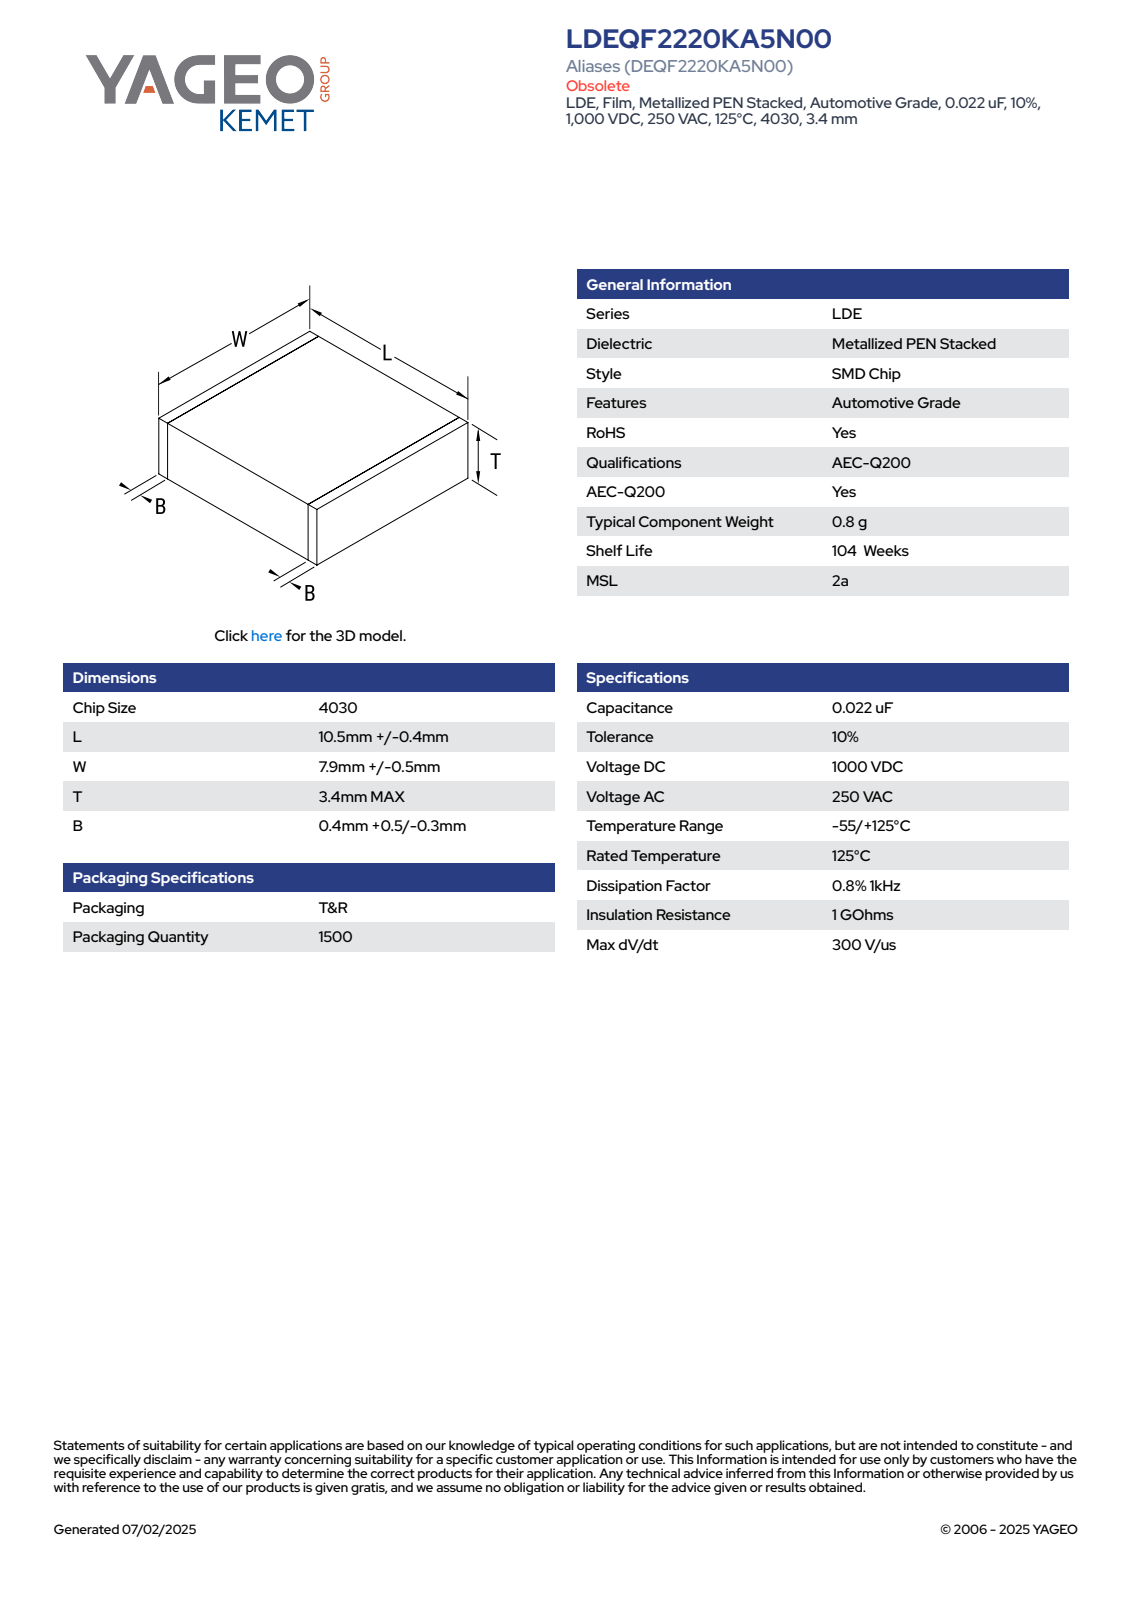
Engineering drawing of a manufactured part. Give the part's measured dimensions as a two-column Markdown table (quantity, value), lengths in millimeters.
| quantity | value |
| --- | --- |
| part name | CFS_LDELDB_4030_L10.9W8.4T3.4B0.9 |
| STEP written by | SolidWorks 2020 (AUTOMOTIVE_DESIGN) |
| units | millimeters |
| bodies | 4 solids, 73 faces (73 planar, 0 cylindrical, 0 other) |
| overall size | 10.9 × 8.4 × 3.4 |
| volume | 309 mm³ |
| surface area | 320 mm² |
| main face-to-face distances | 3.38, 8.38, 10.9, 3.39, 3.4, 8.39, 8.4, 0.5, 10.4, 9.9 |
